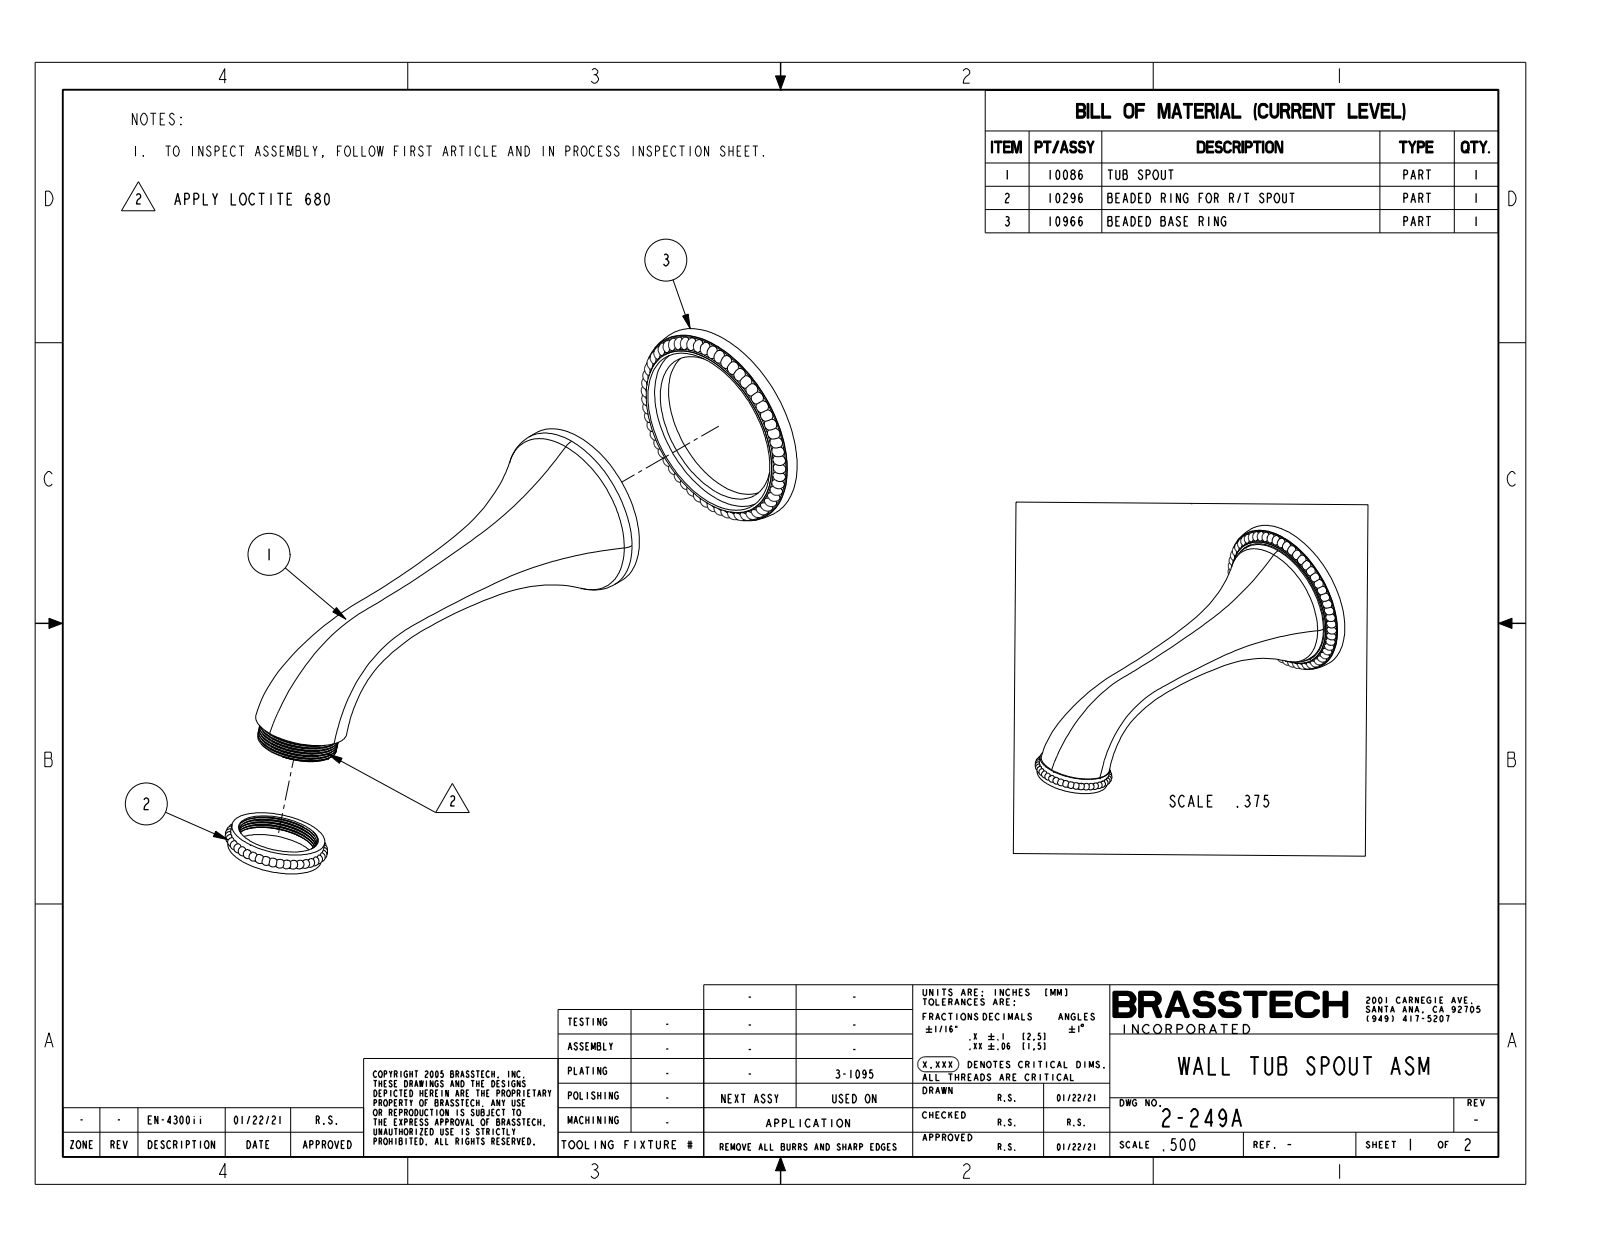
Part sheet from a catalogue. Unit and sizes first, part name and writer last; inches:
Units: inches
Overall size (bounding box): 6.293 × 2.848 × 2.845
Round bosses / shafts (diameter × count): ⌀2.435 ×1, ⌀2.345 ×1, ⌀1.705 ×1, ⌀1.3 ×1, ⌀1.194 ×1, ⌀1.102 ×1
Main face-to-face distances: 0.29, 0.28, 0.16, 0.15, 0.13, 0.313, 0.318, 0.296, 0.291, 0.022
Volume: 9.683 in³ · Surface area: 48.29 in²
Bodies: 3 solids, 349 faces (96 planar, 14 cylindrical, 239 other)
Part name (STEP PRODUCT): 10086; 10296; 10966; 2-249A_ASM
STEP written by: CREO PARAMETRIC BY PTC INC, 2018400 (AUTOMOTIVE_DESIGN)
